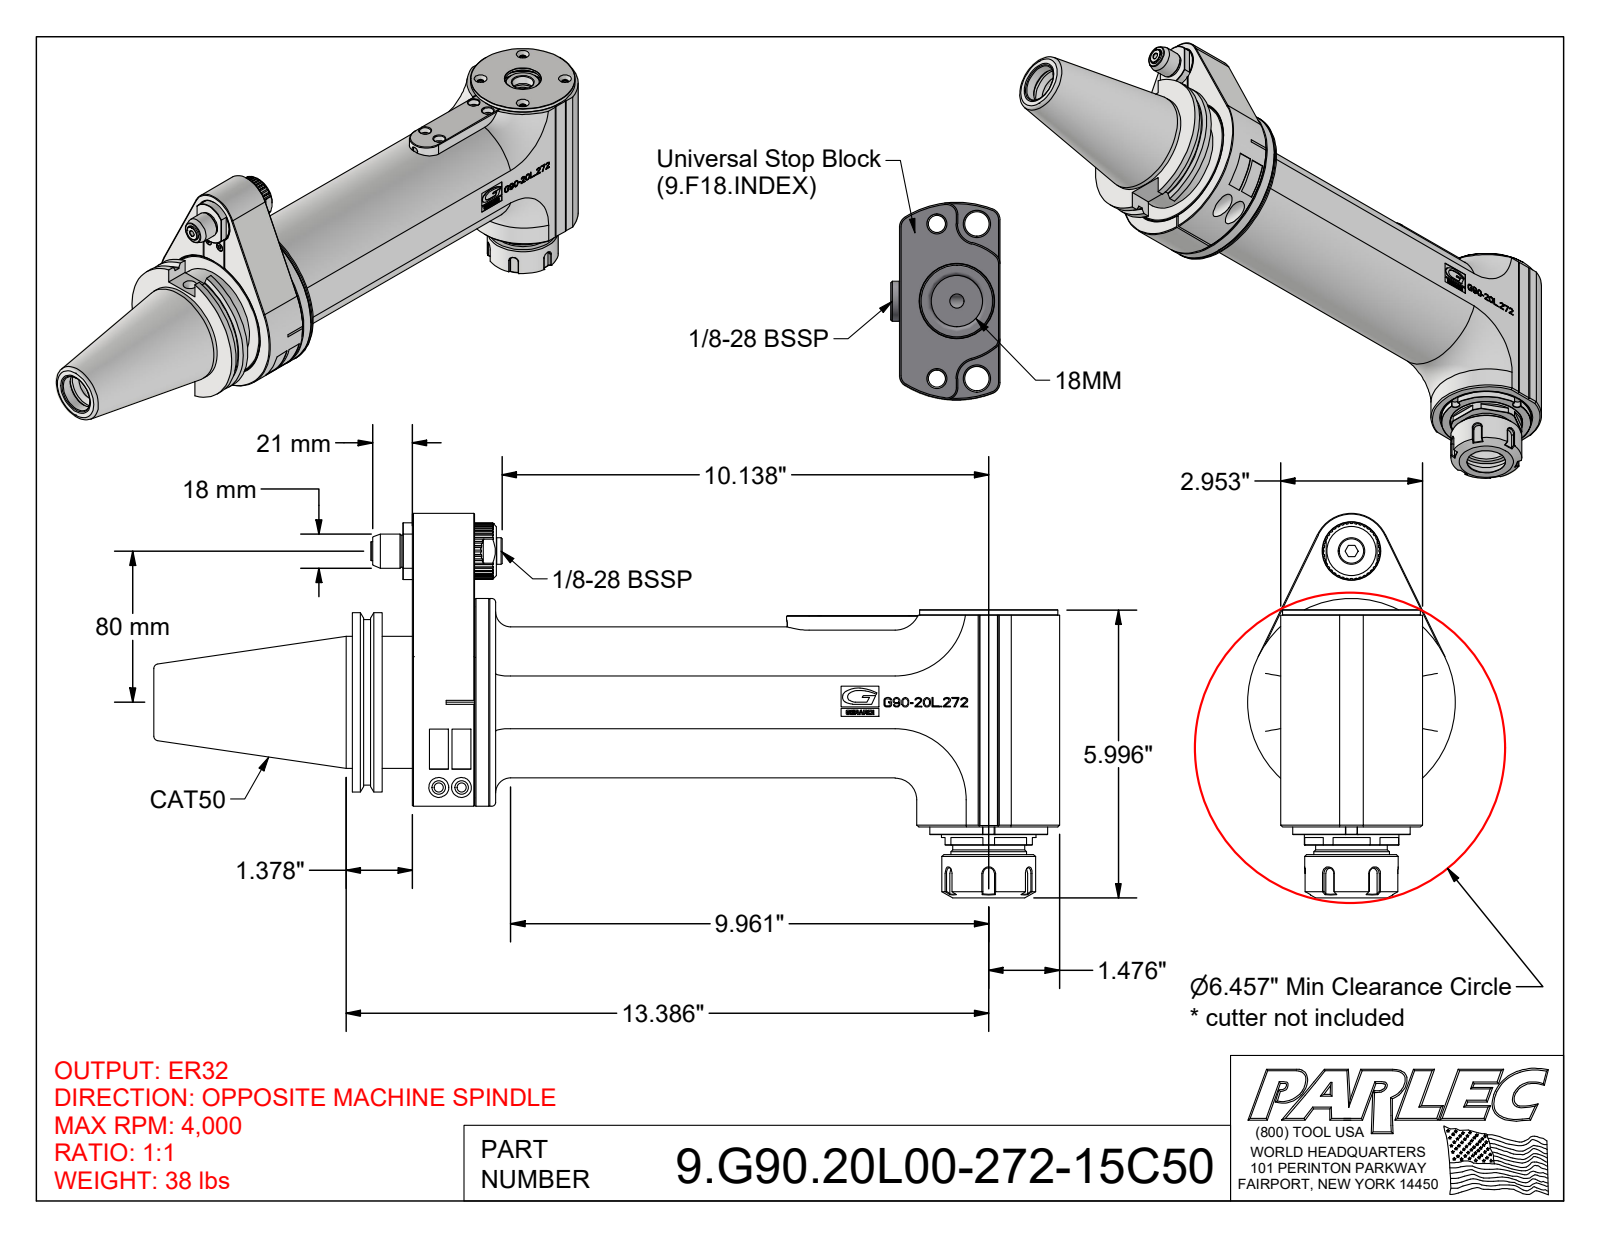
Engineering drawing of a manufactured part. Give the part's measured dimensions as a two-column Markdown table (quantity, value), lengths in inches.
| quantity | value |
| --- | --- |
| part name | 9.G90.20L00-272-15C50; 9_G90_20L00-272; 9_GA2_458_1 (Classic, Type 2, Cat50, 80mm) |
| STEP written by | Autodesk Inventor 2022 (AUTOMOTIVE_DESIGN) |
| units | inches |
| bodies | 20 solids, 1443 faces (854 planar, 261 cylindrical, 328 other) |
| overall size | 18.87 × 8.012 × 4.331 |
| volume | 147.1 in³ |
| surface area | 455.7 in² |
| round holes (diameter × count) | 0.197 × 12, 0.13 × 9, 0.177 × 8, 0.165 × 4, 0.315 × 4, 0.335 × 3, 0.157 × 2, 0.236 × 2, 0.276 × 2, 0.413 × 2, 0.433 × 2, 0.346 × 1 |
| round bosses / shafts (diameter × count) | 0.394 × 2, 4.331 × 1, 4.016 × 1, 3.875 × 1, 3.593 × 1, 3.524 × 1, 3.15 × 1, 2.874 × 1 |
| partial cylindrical surfaces (radius × count) | 0.118 × 10, 0.098 × 5, 0.085 × 2, 0.224 × 2, 0.278 × 2, 0.315 × 2, 0.469 × 2, 0.472 × 2 |
| main face-to-face distances | 1.299, 2.953, 0.315, 0.984, 0.626, 0.197, 0.118, 0.941, 1.567, 1.925 |
| hole center spacings | 1.87, 3.239, 3.74, 0.968, 1.87, 2.645, 0.217, 0.35 |
